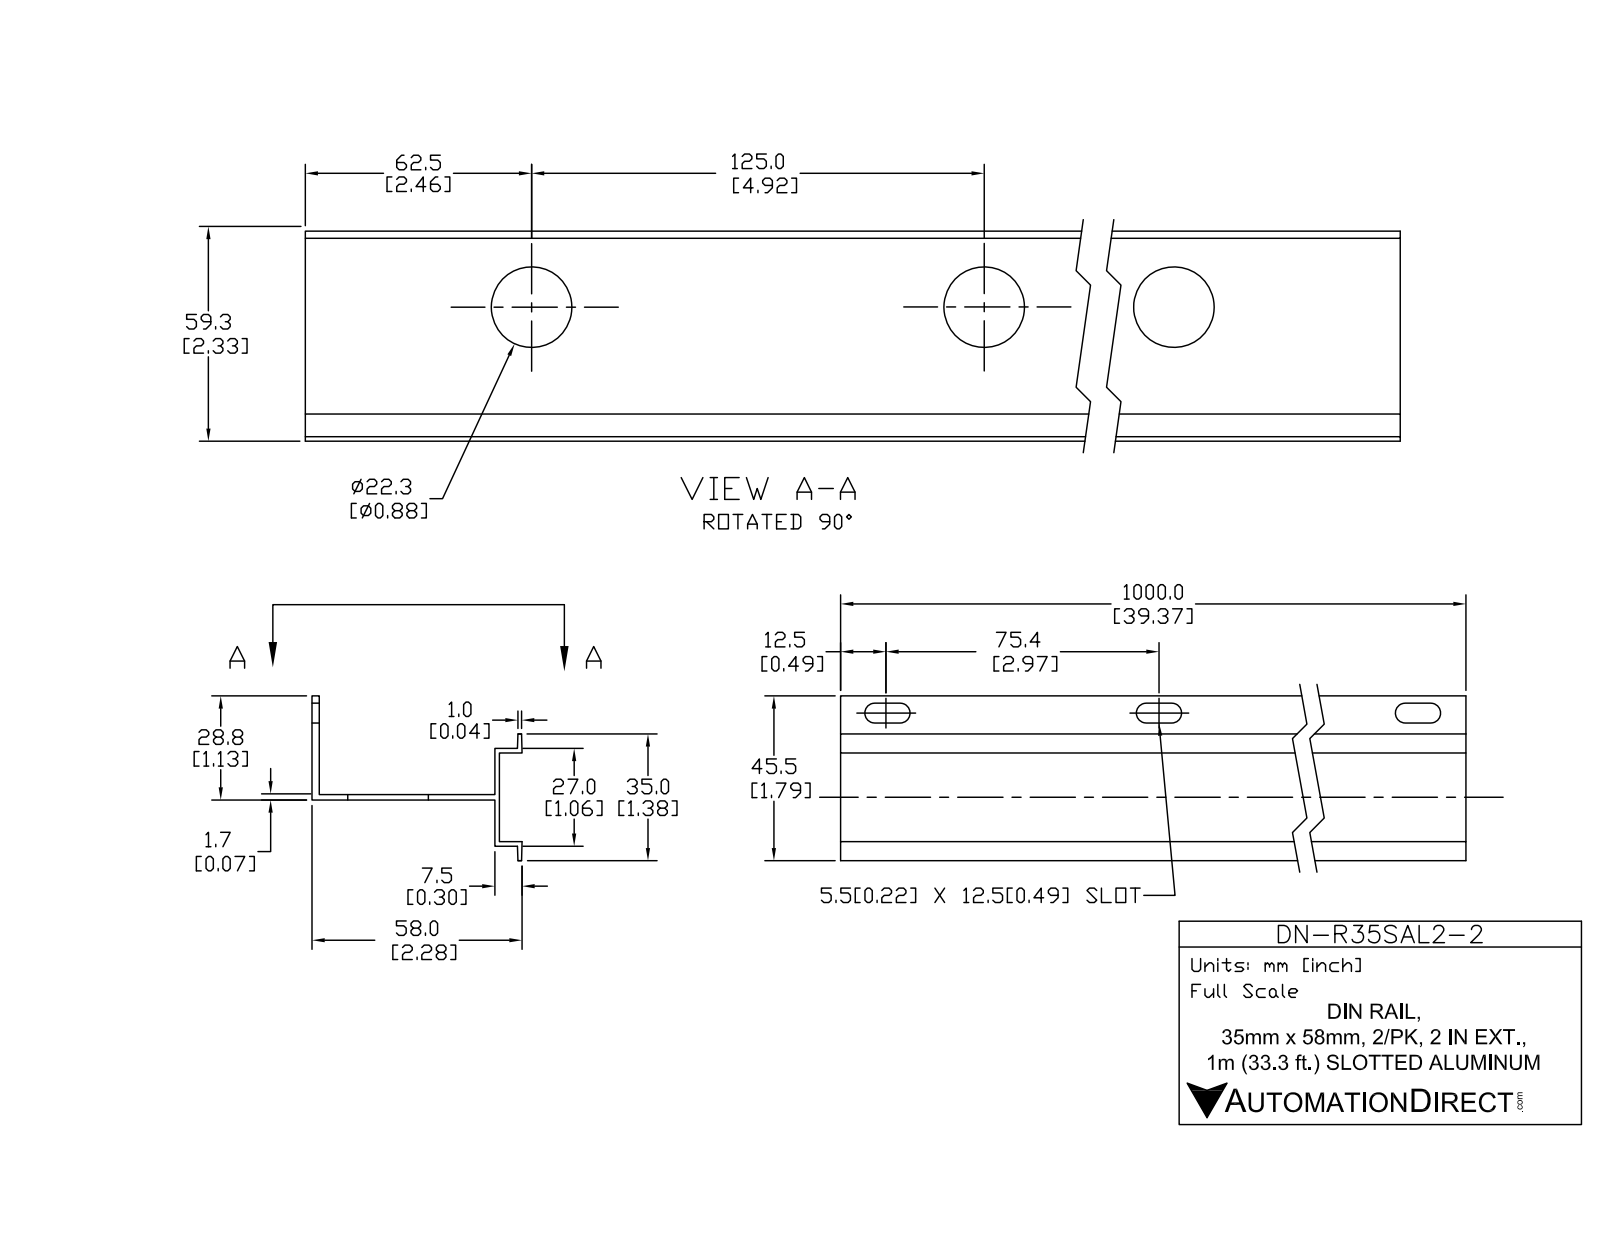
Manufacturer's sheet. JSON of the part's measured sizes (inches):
{"part_name": "DN-R35SAL2", "step_written_by": "SolidWorks 2011 (AUTOMOTIVE_DESIGN)", "units": "inches", "bodies": {"solids": 1, "faces": 84, "planar": 48, "cylindrical": 36, "other": 0}, "overall_size": [39.37, 2.283, 1.791], "volume_in3": 12.79, "surface_area_in2": 382.8, "round_holes": [[0.876, 8]], "partial_cylinders_radius": [[0.108, 28]], "face_to_face_distances": [0.079, 0.049, 1.988, 1.909, 2.037, 1.959, 0.246, 0.443, 0.522, 0.059], "hole_center_spacings": [4.921, 9.843, 14.764, 19.685, 24.606, 29.528, 34.449]}
